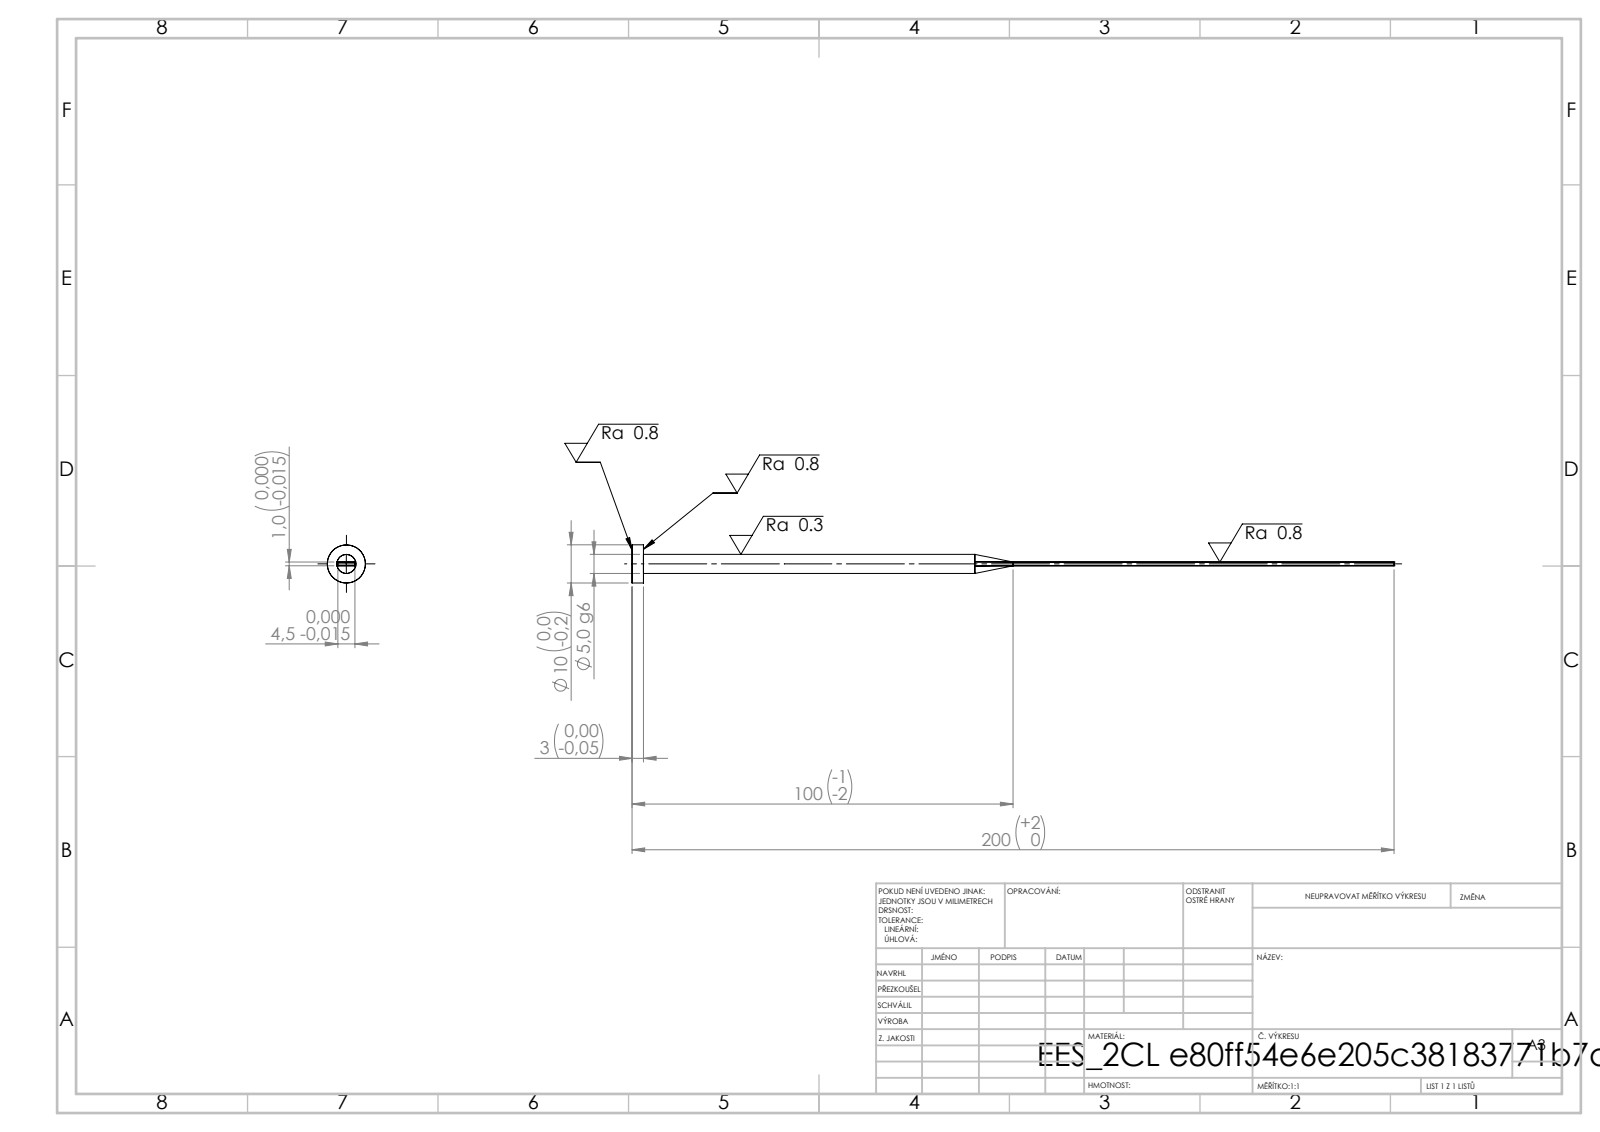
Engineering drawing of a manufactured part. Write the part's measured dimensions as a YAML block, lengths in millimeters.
step_written_by: "SolidWorks 2019 (CONFIG_CONTROL_DESIGN)"
units: millimeters
bodies: {solids: 1, faces: 15, planar: 7, cylindrical: 4, other: 4}
overall_size: [200, 10, 10]
volume: 2508
surface_area: 2832
round_bosses_or_shafts:
  - {diameter: 10, count: 1}
  - {diameter: 5, count: 1}
face_to_face_distances: [1, 4.5, 3, 200, 197]
